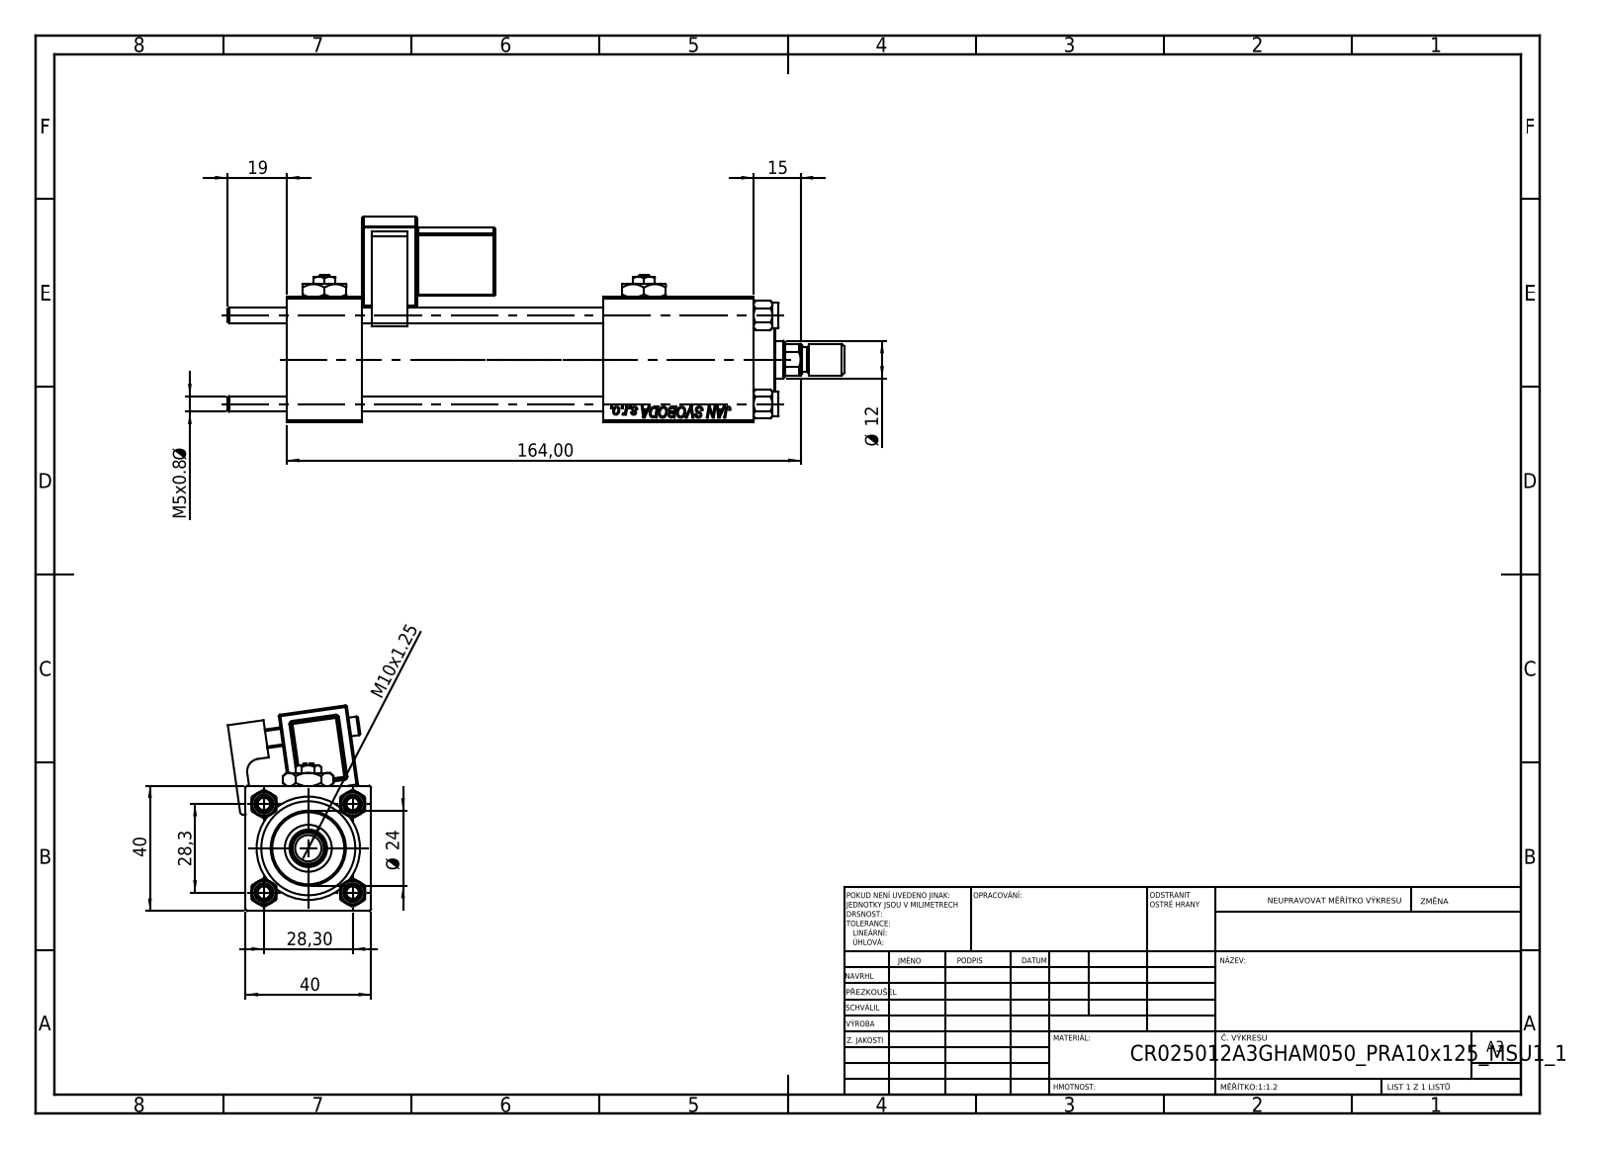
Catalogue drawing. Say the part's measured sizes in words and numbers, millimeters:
The part is named "V215CR_VCP; V215CR_MSU; Zatka_pro_OIL_PORT; ROD_END_AH (+4 more)". Its 3-D file was written by "SolidWorks 2019 (CONFIG_CONTROL_DESIGN)". It is 15 solids with 1325 faces: 599 planar, 124 cylindrical and 602 other. Overall it measures 197 by 65.59 by 45.69 millimeters. Its volume is 178 400 cubic millimeters and its surface area 75 523 square millimeters. Round holes: 4 of diameter 5, 3 of diameter 20, 2 of diameter 7, 2 of diameter 13.16, 1 of diameter 6.5, 1 of diameter 12, 1 of diameter 15, 1 of diameter 25, 1 of diameter 30. Round bosses or shafts: 5 of diameter 8, 1 of diameter 31, 1 of diameter 24, 1 of diameter 10, 1 of diameter 6. Partial cylindrical surfaces (rounded edges, fillets, slot ends): 24 of radius 0.5, 1 of radius 1, 1 of radius 2.5, 1 of radius 4, 1 of radius 5.5. The main face-to-face distances are 40, 24, 3, 39.8, 149, 125, 77, 120.3, 96.3, 28.7. The hole center spacings are 20.01, 28.3, 40.02, 102.
